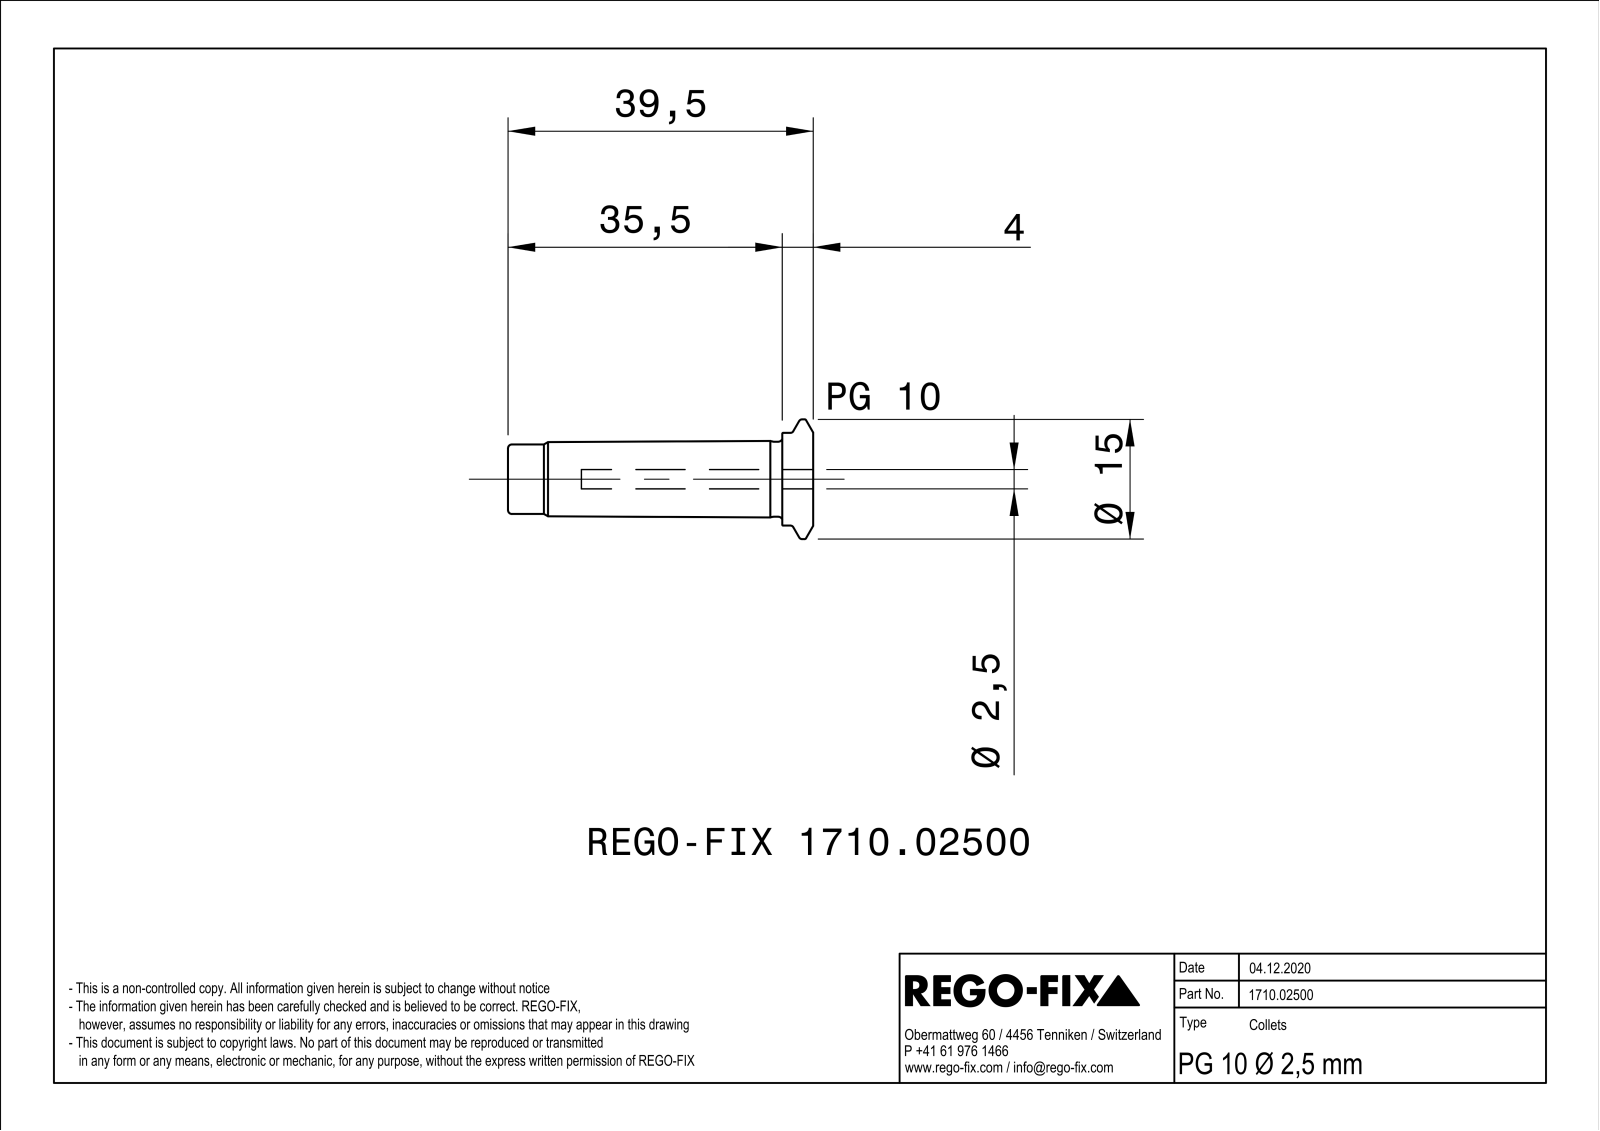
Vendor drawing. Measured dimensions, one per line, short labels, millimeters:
name: NOCUT
written by: SIEMENS PLM Software Solid Edge ST10 (AUTOMOTIVE_DESIGN)
unit: mm
bodies: 0 solids, 60 faces (11 planar, 18 cylindrical, 31 other)
size: 39.5 × 15.5 × 15.49
holes: 1× ⌀2.5, 1× ⌀6.19
bosses: 1× ⌀15.5, 1× ⌀12, 1× ⌀9.7, 1× ⌀9
rounds: 6× R0.4
face distances: 0.8, 39.5, 4, 35.5
